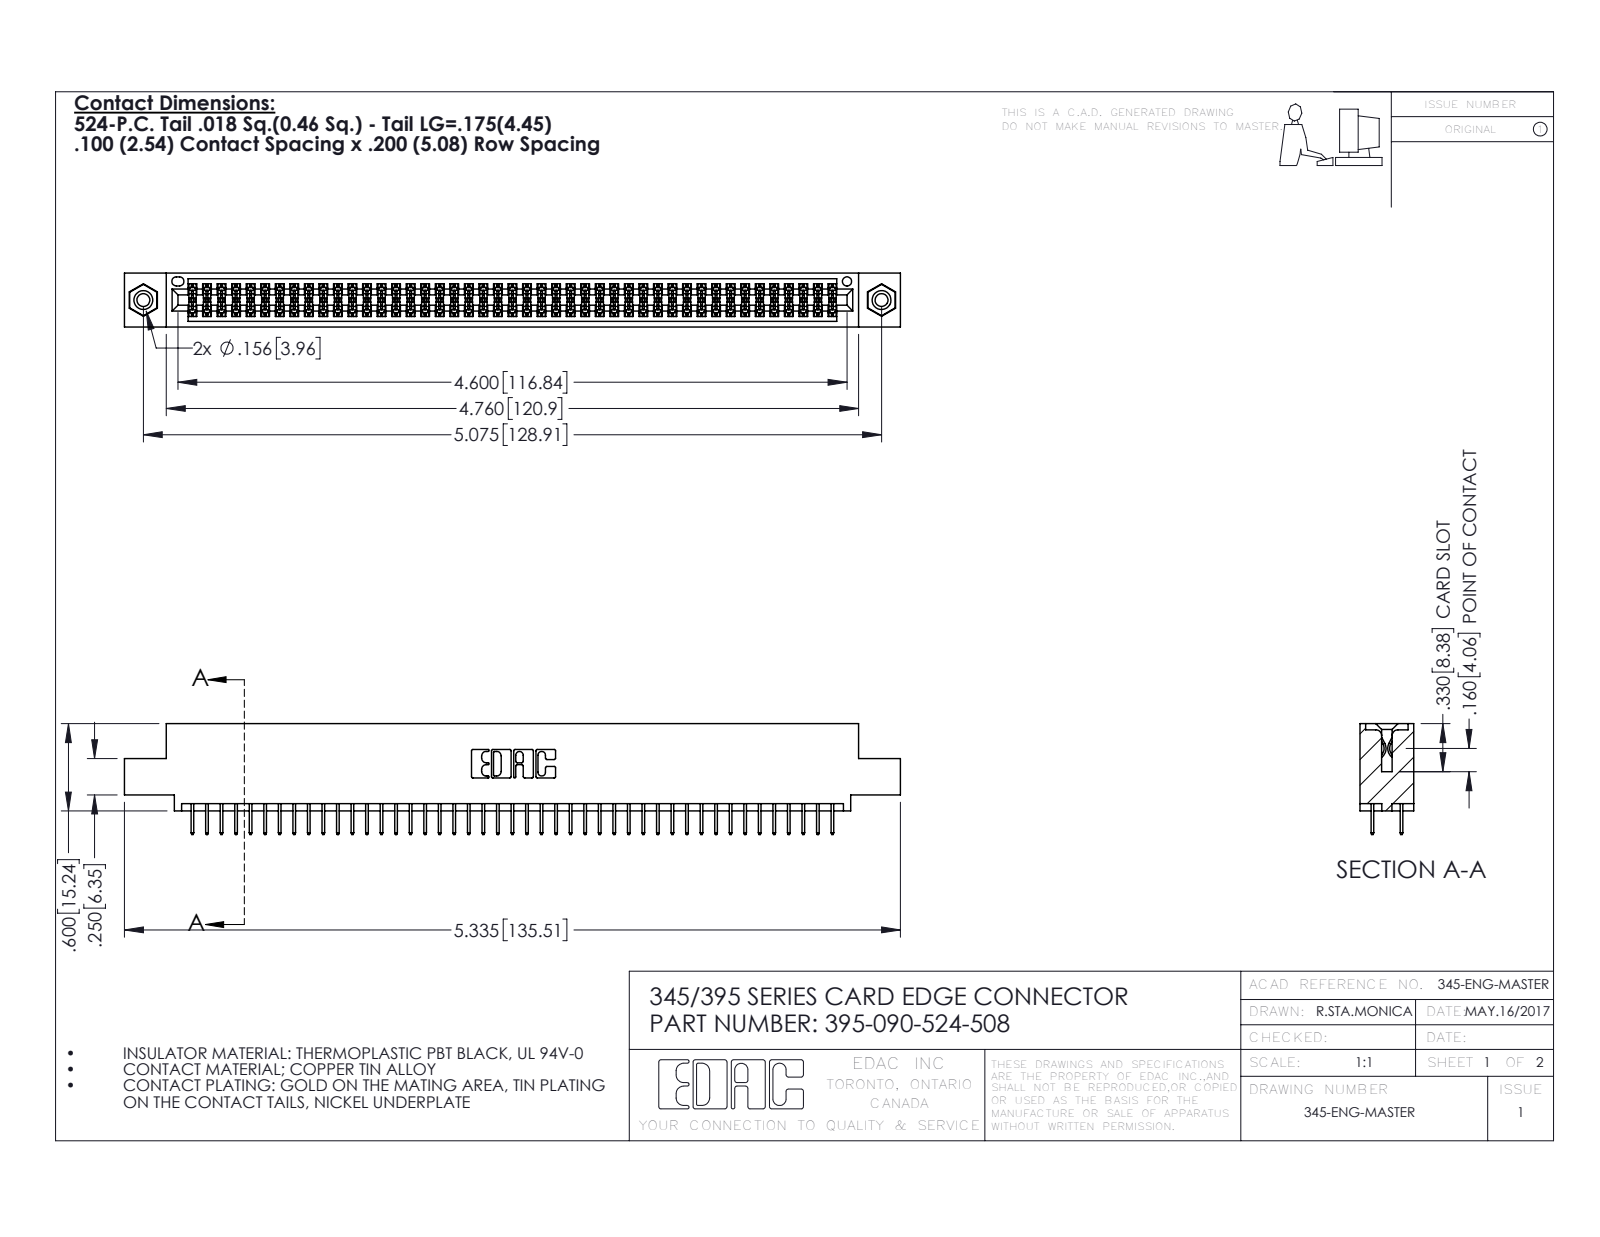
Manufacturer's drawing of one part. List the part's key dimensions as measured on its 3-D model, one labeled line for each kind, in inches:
Part name (STEP PRODUCT): 345 Part_0.110 Offset - 0.156 Dia-TI; 345-250-001_345-250-003-102; 395-090-524-508; 345-292-001_345-293-124
STEP written by: SolidWorks 2016 (CONFIG_CONTROL_DESIGN)
Units: inches
Bodies: 93 solids, 5050 faces (3626 planar, 1408 cylindrical, 16 other)
Overall size (bounding box): 5.335 × 0.762 × 0.37
Volume: 0.792 in³ · Surface area: 29.43 in²
Round holes (diameter × count): ⌀0.089 ×2, ⌀0.125 ×2, ⌀0.156 ×2, ⌀0.064 ×1
Round bosses / shafts (diameter × count): ⌀0.155 ×2
Partial cylindrical surfaces — rounded edges, fillets, slot ends (radius × count): R0.006 ×135, R0.01 ×22, R0.007 ×6, R0.031 ×6, R0.026 ×3, R0.014 ×2, R0.019 ×2, R0.022 ×2
Main face-to-face distances: 0.072, 0.298, 0.2, 0.37, 0.098, 0.272, 0.025, 0.225, 0.072, 0.175
Hole centre spacings: 0.27, 4.839, 5.075
